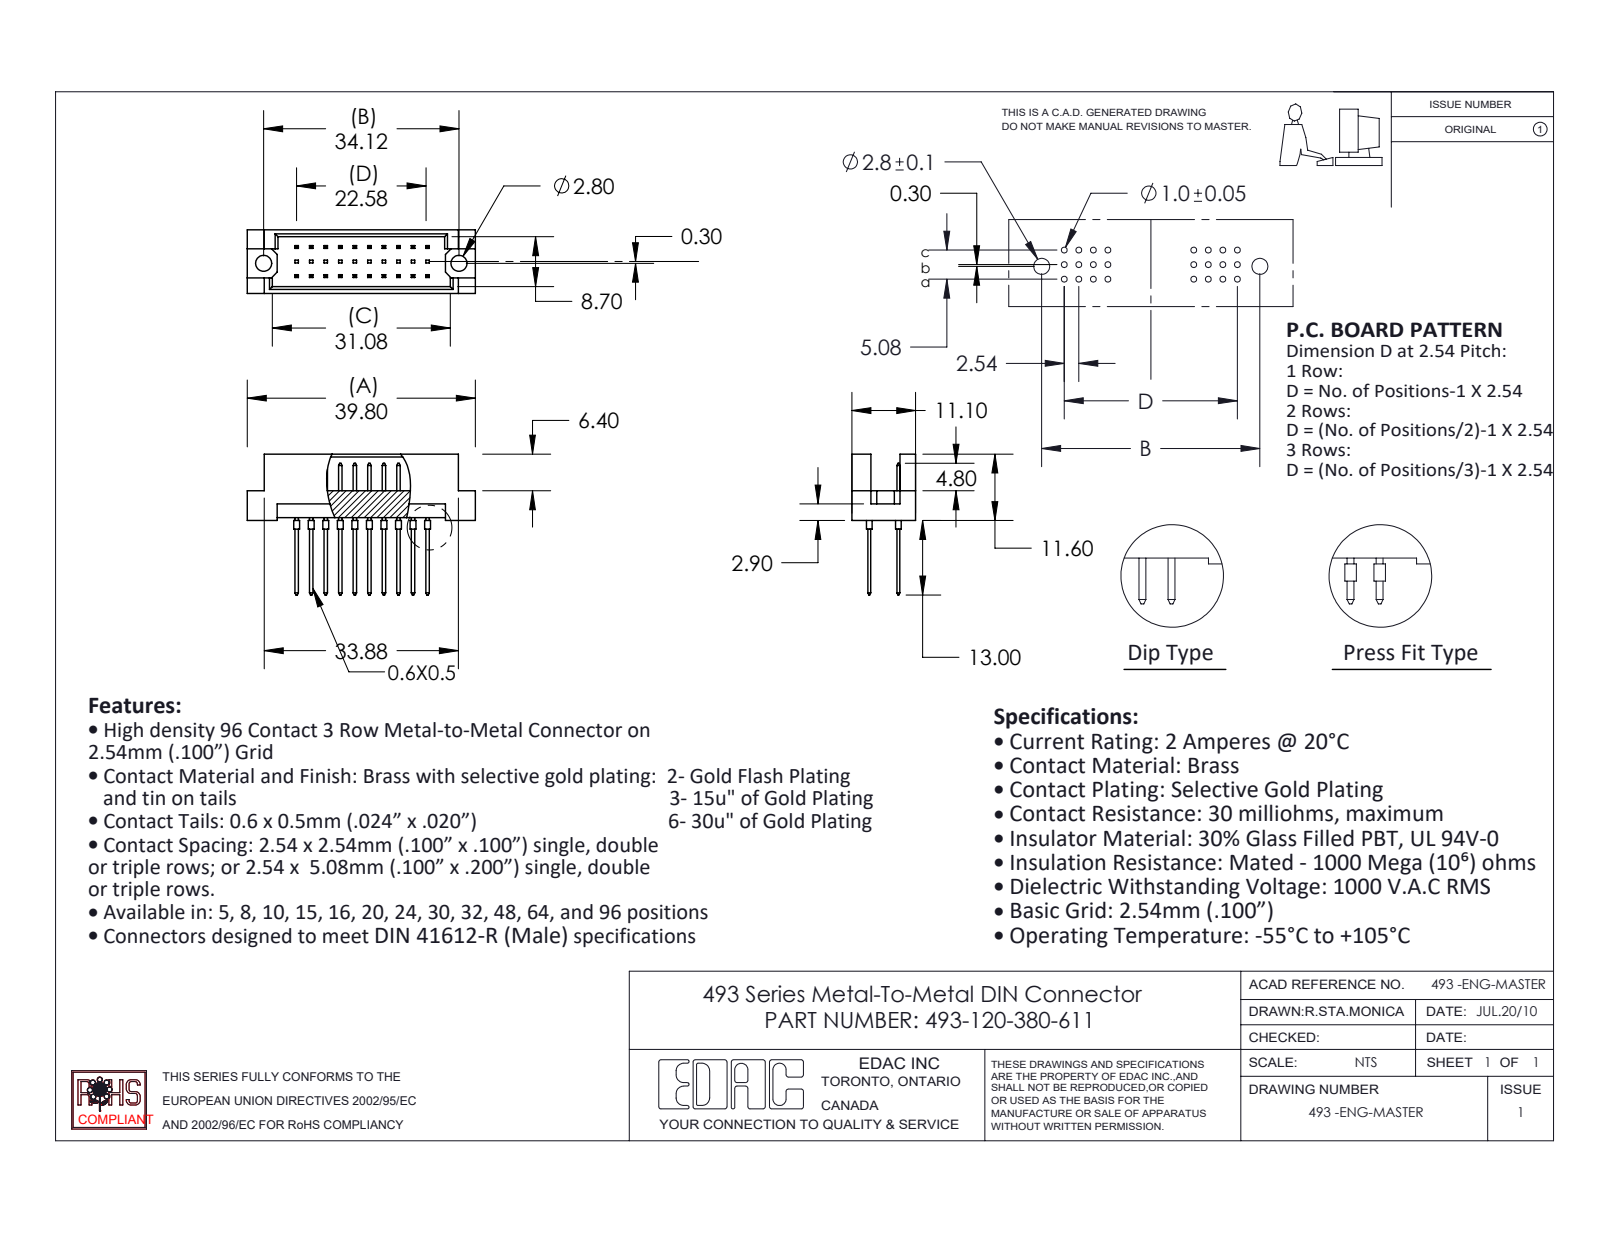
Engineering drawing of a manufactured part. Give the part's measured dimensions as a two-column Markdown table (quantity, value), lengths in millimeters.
| quantity | value |
| --- | --- |
| part name | 493 Part_30; 493-120-380-611; 493-290_80 |
| STEP written by | SolidWorks 2020 (CONFIG_CONTROL_DESIGN) |
| units | millimeters |
| bodies | 21 solids, 612 faces (568 planar, 44 cylindrical, 0 other) |
| overall size | 39.8 × 24.6 × 11.1 |
| volume | 2 523 mm³ |
| surface area | 3 790 mm² |
| round holes (diameter × count) | 2.8 × 2 |
| round bosses / shafts (diameter × count) | 1 × 20 |
| main face-to-face distances | 5.08, 2.54, 1.2, 9.9, 0.5, 11.1, 2.76, 3.26, 7.84, 8.34 |
| hole center spacings | 34.12 |
